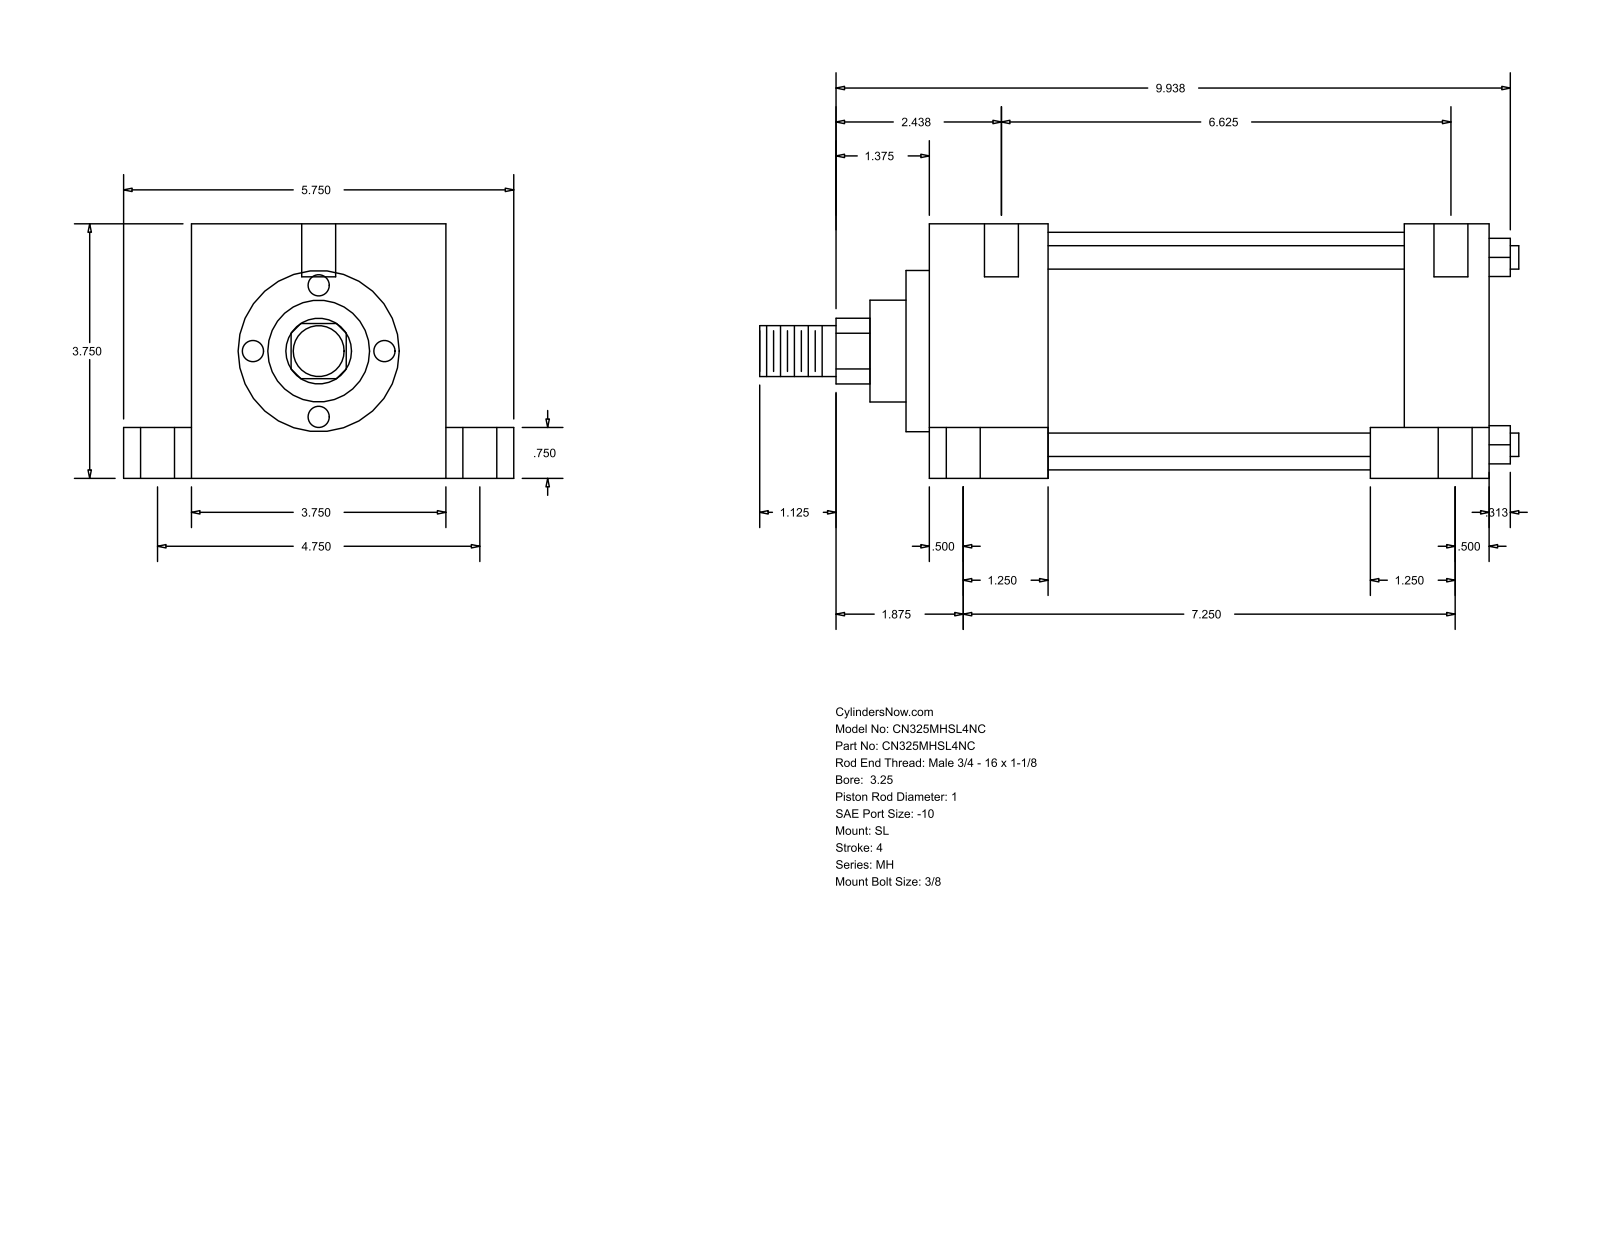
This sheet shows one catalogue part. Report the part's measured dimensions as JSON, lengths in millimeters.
{"part_name": "MH_SL__0325_1", "step_written_by": "GSSL Pune (CONFIG_CONTROL_DESIGN)", "units": "millimeters", "bodies": {"solids": 0, "faces": 110, "planar": 77, "cylindrical": 33, "other": 0}, "overall_size": [284.16, 146.05, 95.25], "round_holes": [[12.7, 6], [5.56, 4], [19.05, 4]], "round_bosses_or_shafts": [[8.76, 4], [88.9, 1], [60.33, 1], [38.1, 1], [25.4, 1], [19.05, 1]], "partial_cylinders_radius": [[12.29, 1]], "face_to_face_distances": [95.24, 209.55, 120.65, 44.46, 165.09, 25.41, 19.05, 76.19, 177.8, 133.34], "hole_center_spacings": [60.35, 60.41, 61.65, 62, 120.66, 174.62, 180.27, 181.75]}
